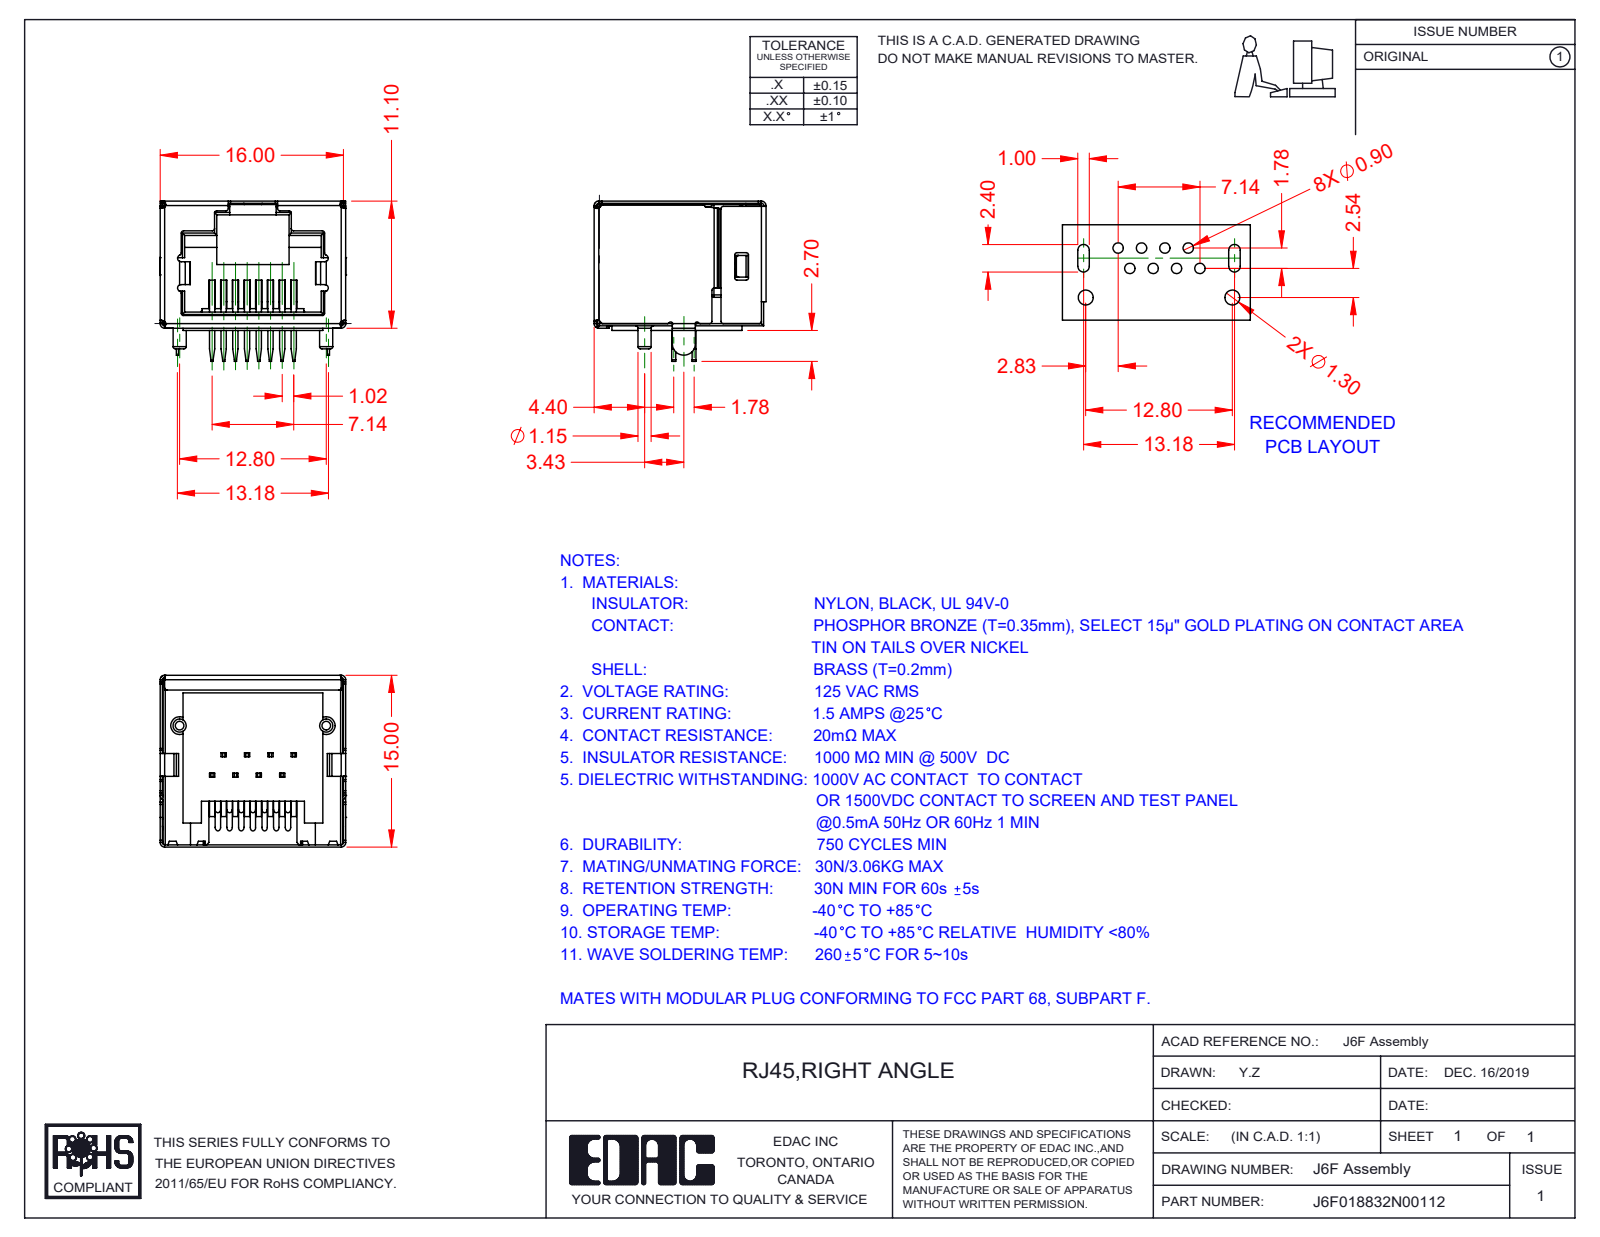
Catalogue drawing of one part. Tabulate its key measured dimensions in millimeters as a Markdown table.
| quantity | value |
| --- | --- |
| part name | J6F018832N00112; 6F Shield; 6F Contacts; 6F Insulator |
| STEP written by | SolidWorks 2016 (CONFIG_CONTROL_DESIGN) |
| units | millimeters |
| bodies | 10 solids, 960 faces (695 planar, 223 cylindrical, 42 other) |
| overall size | 16.2 × 15 × 14 |
| volume | 1 336 mm³ |
| surface area | 3 711 mm² |
| round bosses / shafts (diameter × count) | 1.15 × 2 |
| partial cylindrical surfaces (radius × count) | 0.2 × 77, 0.4 × 24, 0.3 × 20, 0.5 × 9, 0.23 × 7, 0.15 × 5, 0.1 × 4, 1 × 3 |
| main face-to-face distances | 15.75, 16, 15.95, 11, 15.7, 9.7, 11.1, 16.2, 15.8, 1.2 |
